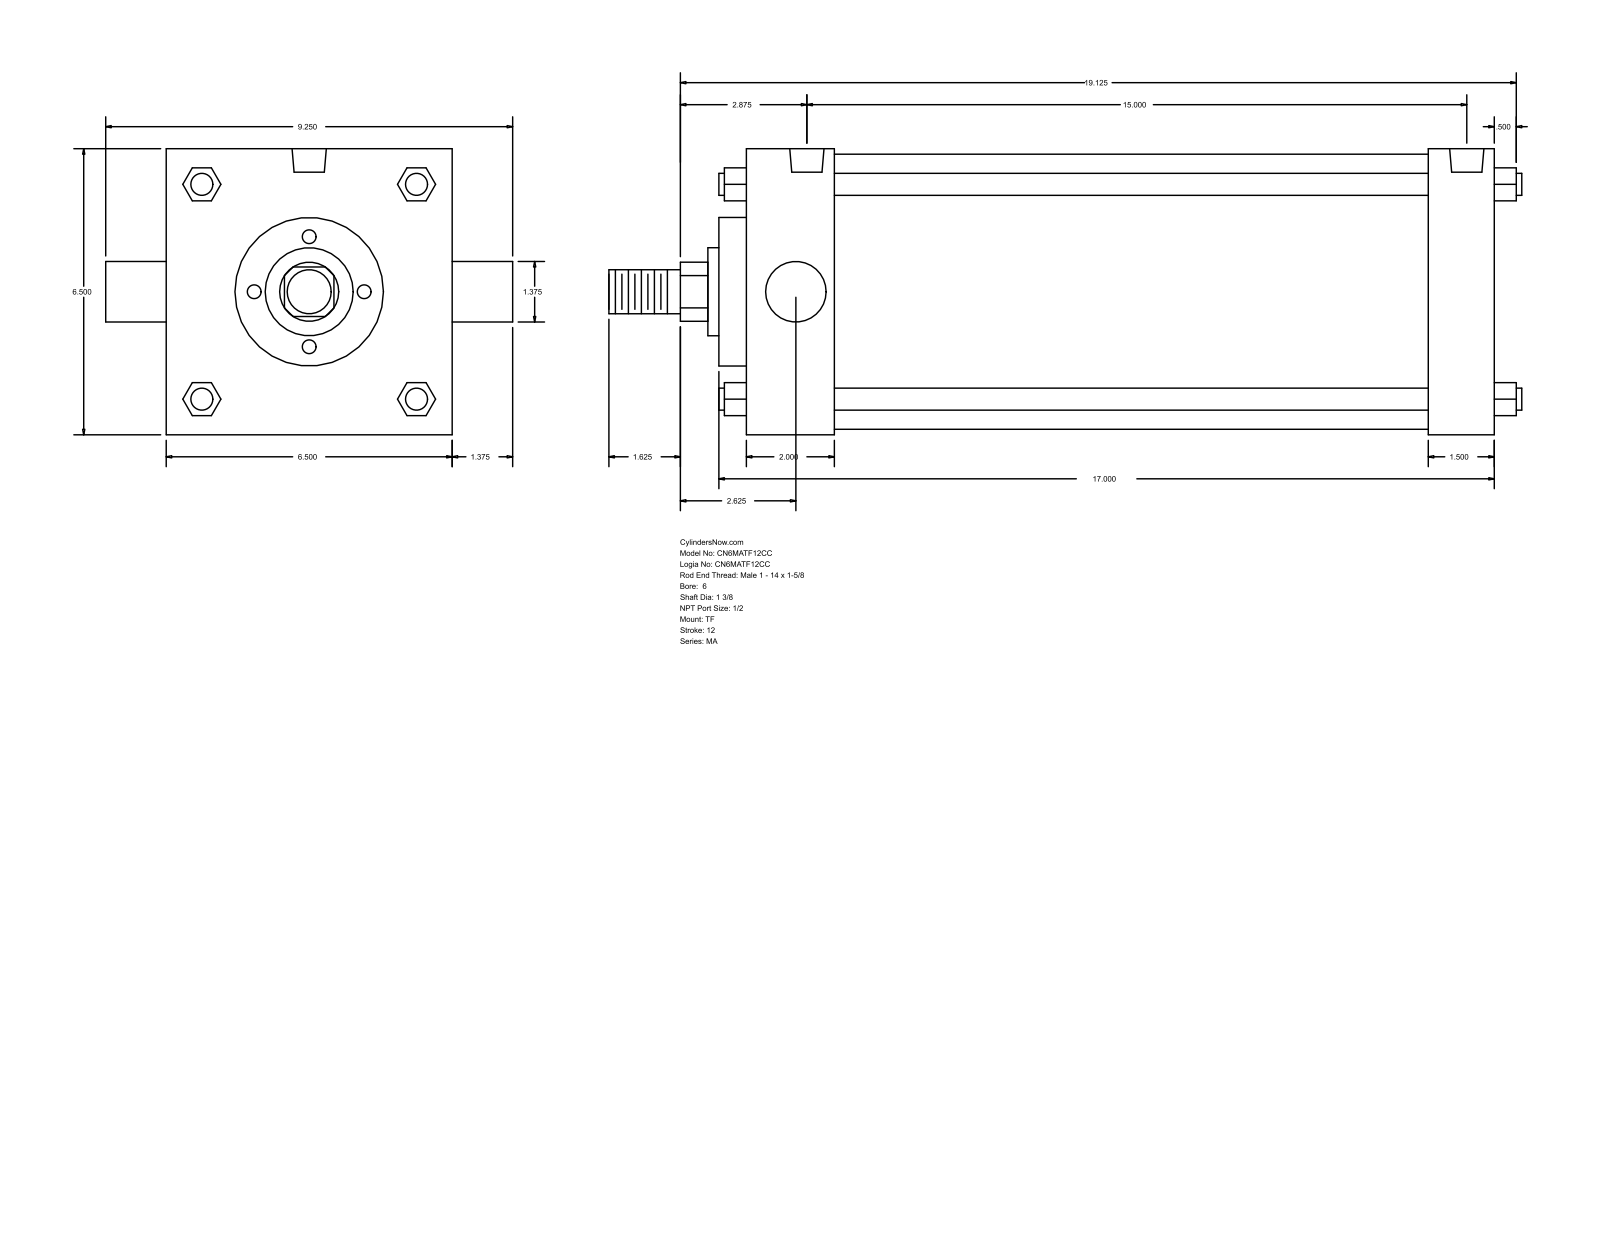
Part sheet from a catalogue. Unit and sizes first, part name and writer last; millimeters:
Units: millimetres
Overall size (bounding box): 527.05 × 234.95 × 165.1
Round holes (diameter × count): ⌀17.46 ×3, ⌀19.77 ×2
Round bosses / shafts (diameter × count): ⌀12.7 ×4, ⌀34.92 ×2, ⌀158.75 ×1, ⌀85.72 ×1, ⌀50.8 ×1, ⌀25.4 ×1
Partial cylindrical surfaces — rounded edges, fillets, slot ends (radius × count): R17.06 ×1
Main face-to-face distances: 165.1, 434.97, 50.8, 384.17, 396.88, 346.08, 38.09, 66.67, 15.87, 412.75
Hole centre spacings: 3.18, 380.99, 384.17
Bodies: 0 solids, 122 faces (93 planar, 29 cylindrical, 0 other)
Part name (STEP PRODUCT): MA_TF__0600_1.375
STEP written by: GSSL Pune (CONFIG_CONTROL_DESIGN)
